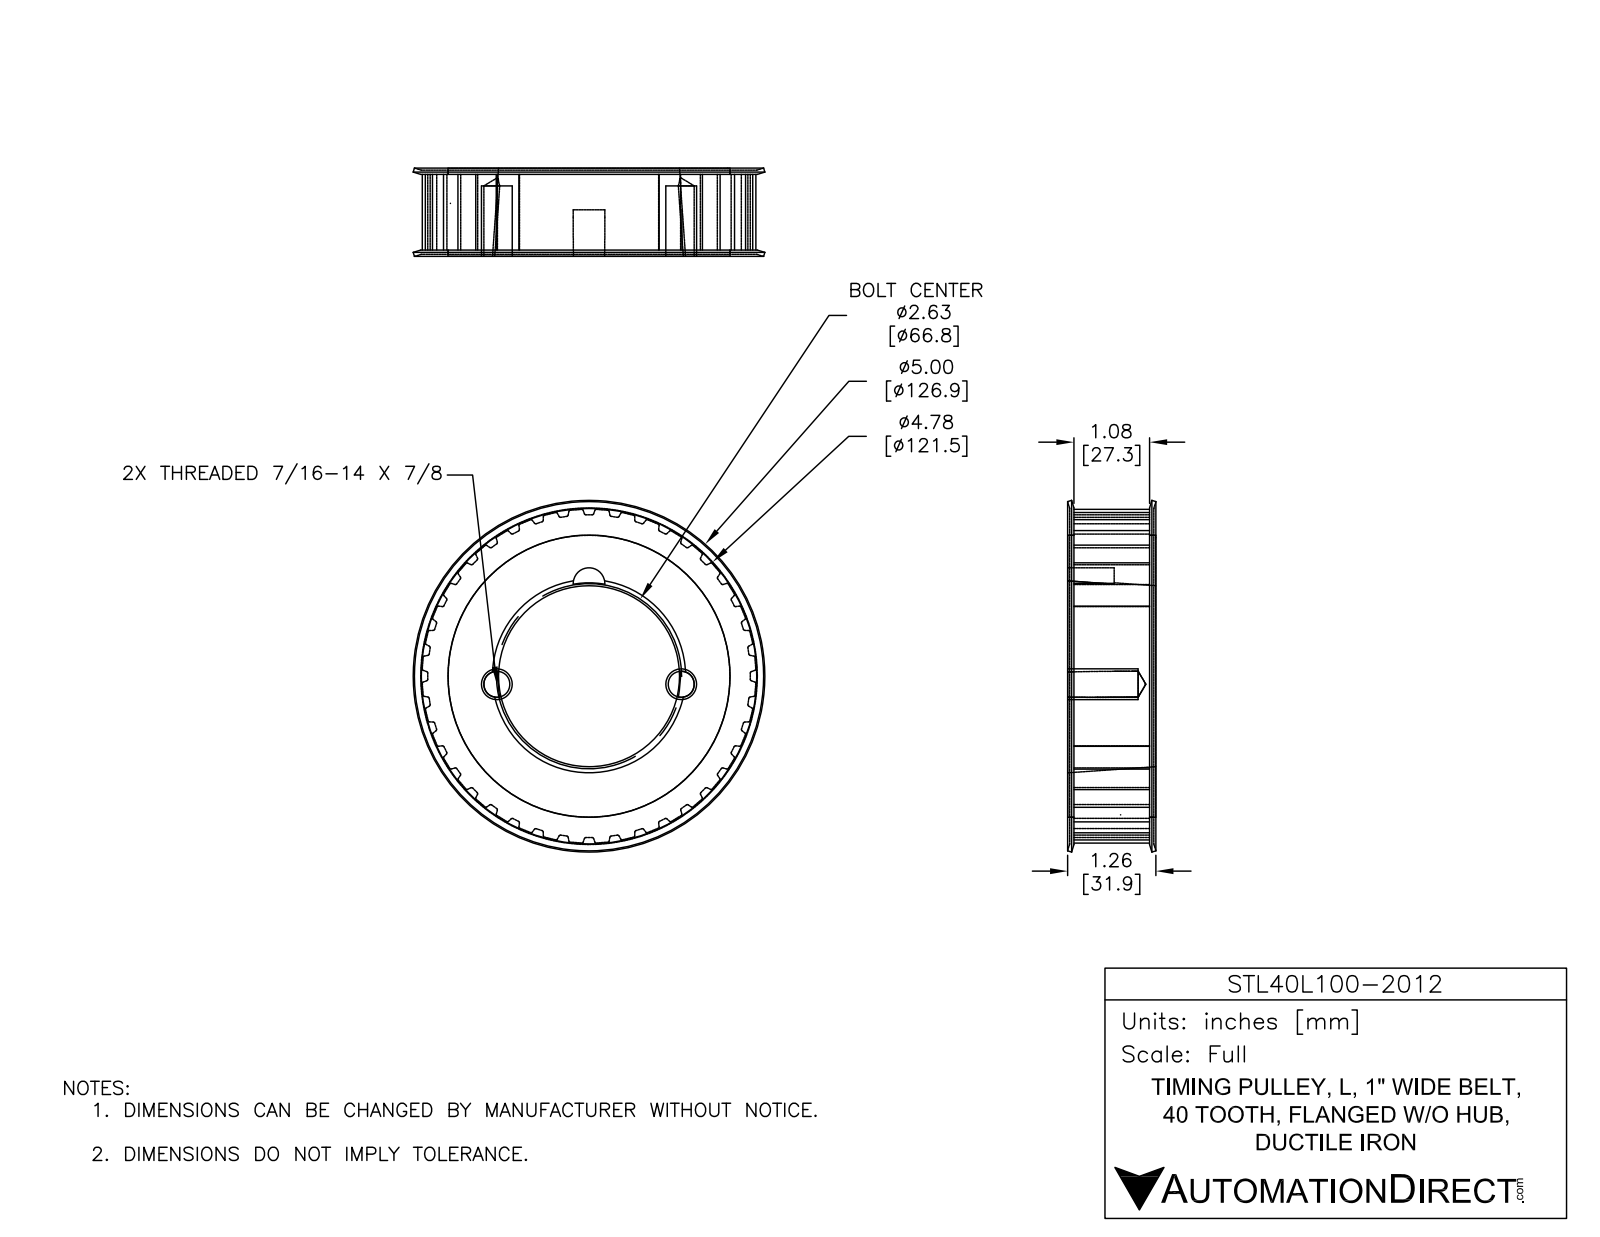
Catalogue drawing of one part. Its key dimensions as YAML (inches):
part_name: "STL40L100AF-2012"
step_written_by: "SolidWorks 2018 (AUTOMOTIVE_DESIGN)"
units: inches
bodies: {solids: 1, faces: 391, planar: 129, cylindrical: 244, other: 18}
overall_size: [4.997, 4.997, 1.255]
volume: 14.45
surface_area: 69.46
round_holes:
  - {diameter: 4.004, count: 1}
round_bosses_or_shafts:
  - {diameter: 4, count: 1}
partial_cylinders:
  - {radius: 0.015, count: 80}
  - {radius: 0.02, count: 80}
  - {radius: 0.185, count: 2}
  - {radius: 0.225, count: 1}
  - {radius: 2.372, count: 1}
  - {radius: 2.372, count: 1}
face_to_face_distances: [0.028, 1.222, 1.25, 1.195, 0.087, 1.163, 0.06, 1.135, 1.075, 4.585]
